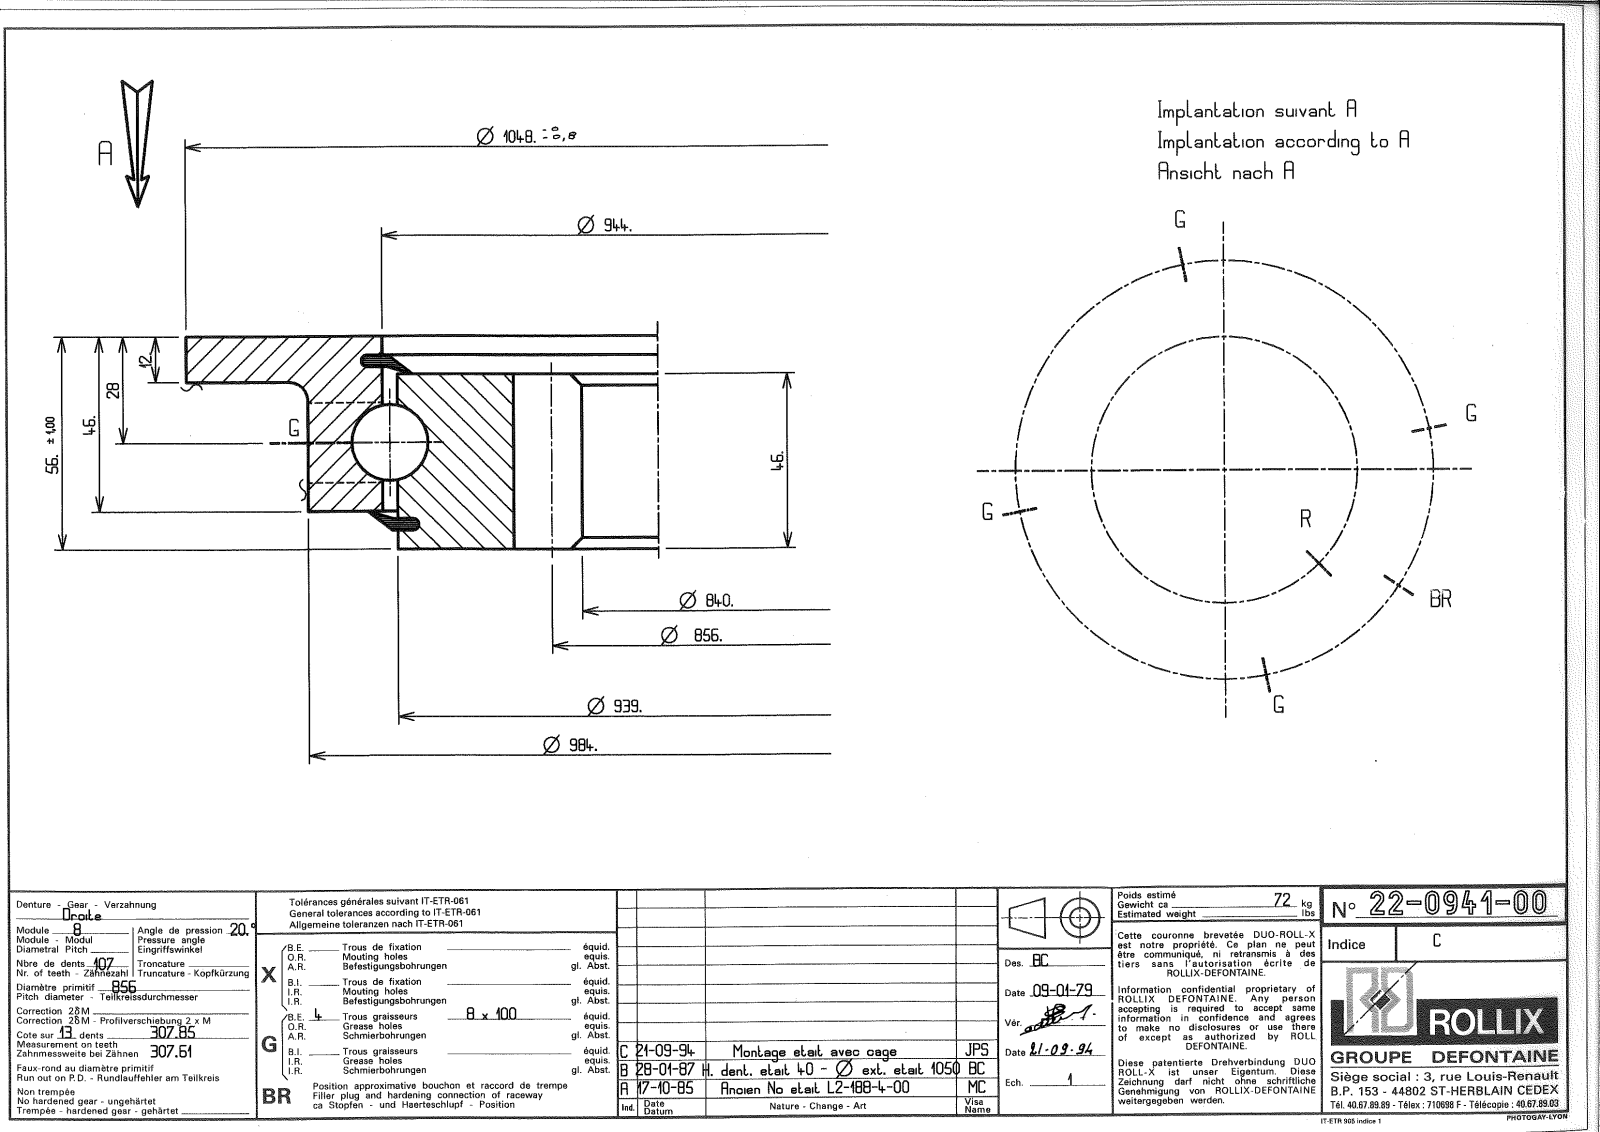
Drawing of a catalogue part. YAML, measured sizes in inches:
part_name: "22-0941-00"
step_written_by: "SolidWorks 2016 (CONFIG_CONTROL_DESIGN)"
units: inches
bodies: {solids: 9, faces: 799, planar: 267, cylindrical: 247, other: 285}
overall_size: [41.26, 41.26, 2.205]
volume: 520.8
surface_area: 2280
round_holes:
  - {diameter: 0.276, count: 4}
  - {diameter: 37.224, count: 1}
round_bosses_or_shafts:
  - {diameter: 0.315, count: 4}
  - {diameter: 41.26, count: 1}
  - {diameter: 38.74, count: 1}
  - {diameter: 36.87, count: 1}
partial_cylinders:
  - {radius: 16.535, count: 1}
  - {radius: 17.244, count: 1}
face_to_face_distances: [0.394, 1.811, 2.205, 1.732, 0.079, 0.472, 1.339, 1.417, 0.195, 2.01]
hole_center_spacings: [0.026]
